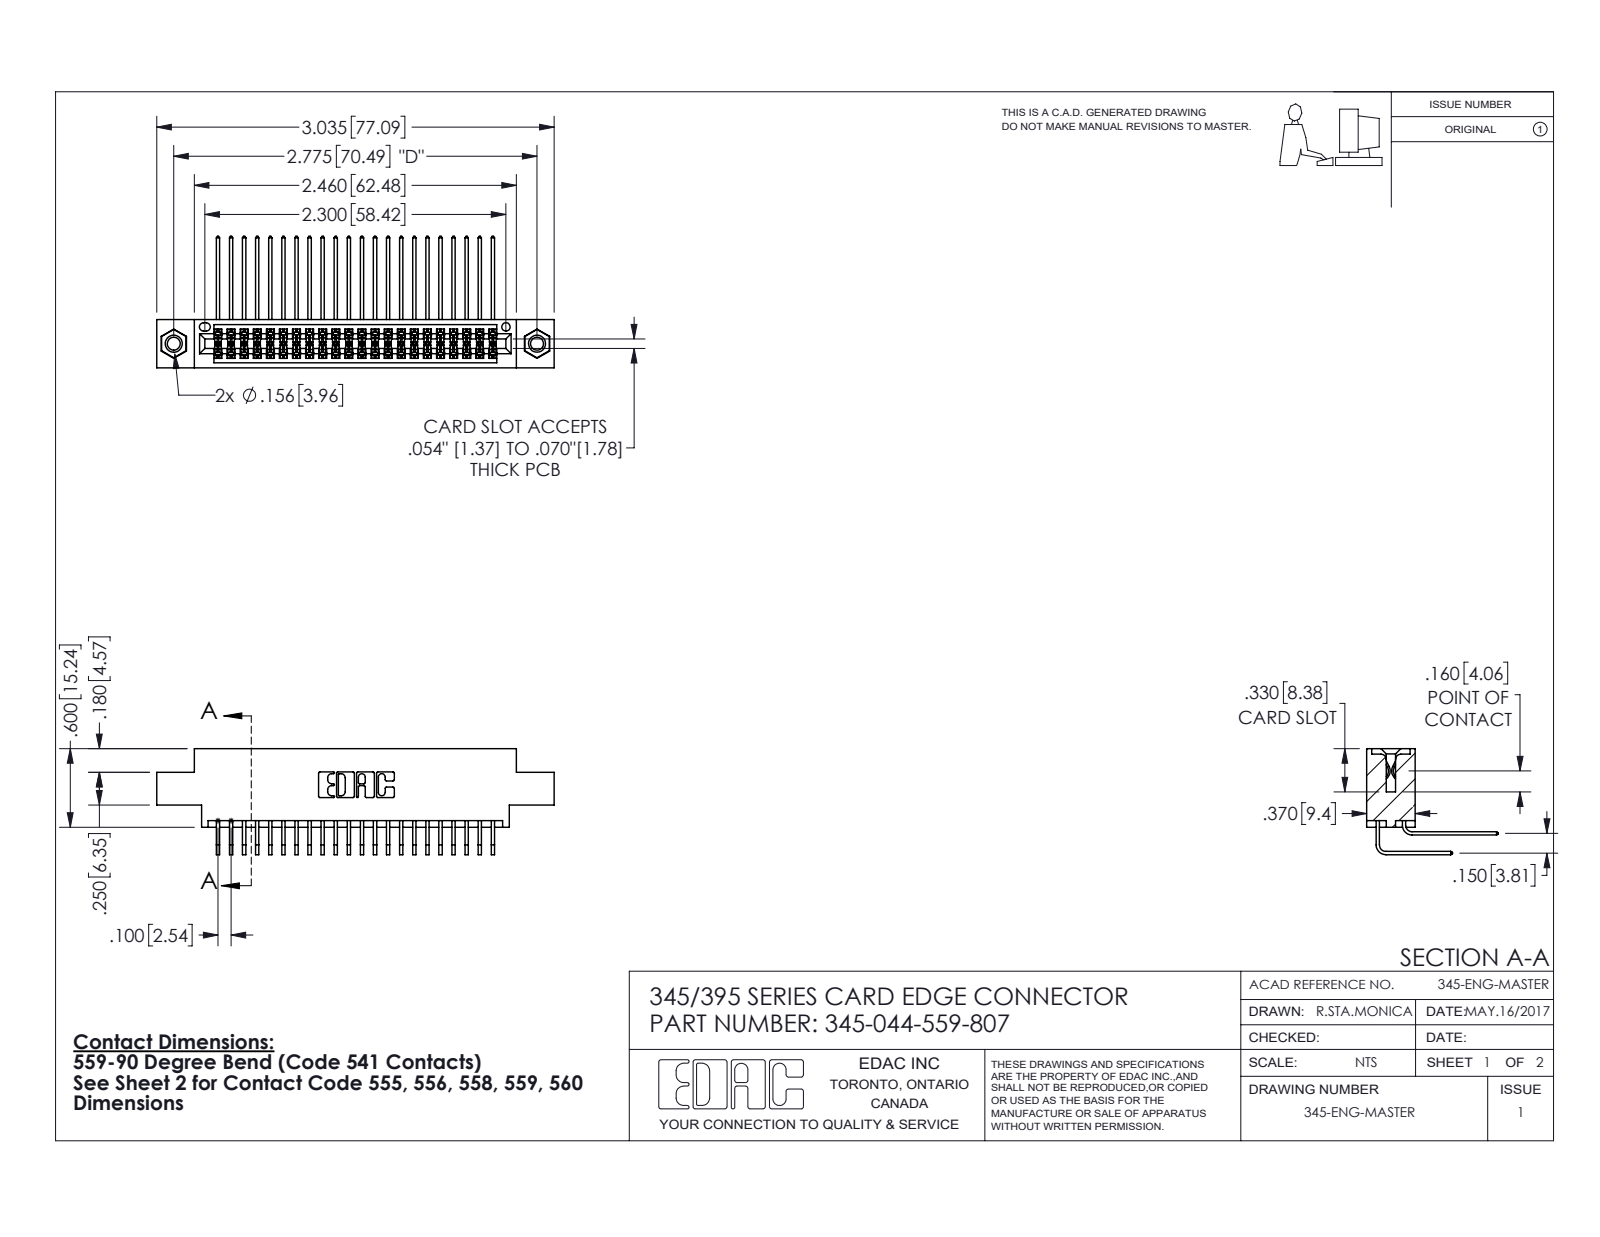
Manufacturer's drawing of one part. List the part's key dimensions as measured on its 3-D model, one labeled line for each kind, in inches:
Part name (STEP PRODUCT): 345-044-559-807; 345-250-001_345-250-005-103; 345-292-001_559 Tail - 2; 345 Part_0.170 Offset - 0.156 Dia-TI (+1 more)
STEP written by: SolidWorks 2016 (CONFIG_CONTROL_DESIGN)
Units: inches
Bodies: 47 solids, 2478 faces (1656 planar, 806 cylindrical, 16 other)
Overall size (bounding box): 3.035 × 1.005 × 0.809
Volume: 0.453 in³ · Surface area: 18.54 in²
Round holes (diameter × count): ⌀0.098 ×2, ⌀0.125 ×2, ⌀0.156 ×2, ⌀0.064 ×1
Round bosses / shafts (diameter × count): ⌀0.155 ×2
Partial cylindrical surfaces — rounded edges, fillets, slot ends (radius × count): R0.006 ×87, R0.01 ×22, R0.007 ×6, R0.031 ×6, R0.026 ×3, R0.014 ×2, R0.019 ×2, R0.022 ×2
Main face-to-face distances: 0.072, 0.298, 0.37, 0.2, 0.098, 0.272, 0.025, 0.15, 0.225, 0.175
Hole centre spacings: 0.27, 2.541, 2.775
